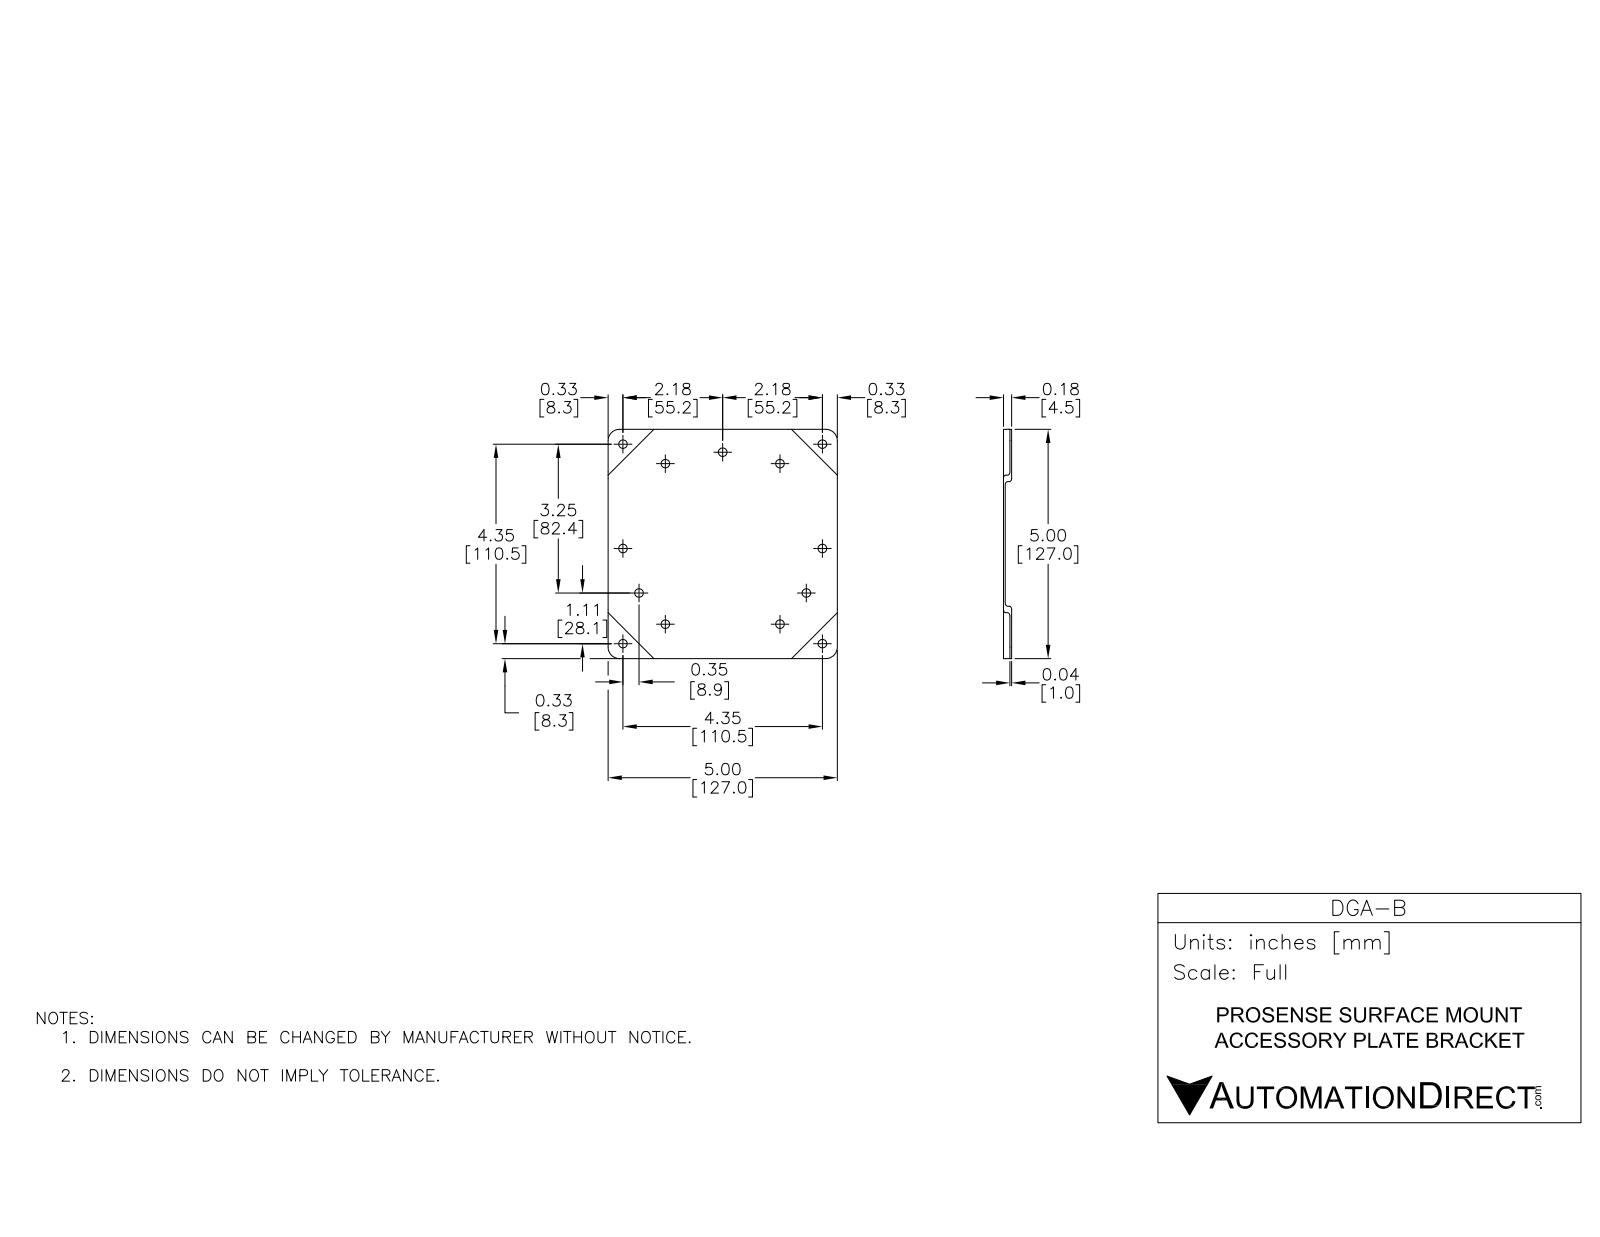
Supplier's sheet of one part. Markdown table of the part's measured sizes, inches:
| quantity | value |
| --- | --- |
| part name | DGA-B |
| STEP written by | SolidWorks 2017 (AUTOMOTIVE_DESIGN) |
| units | inches |
| bodies | 1 solid, 68 faces (22 planar, 46 cylindrical, 0 other) |
| overall size | 5 × 5 × 0.188 |
| volume | 1.987 in³ |
| surface area | 52.23 in² |
| round holes (diameter × count) | 0.187 × 13 |
| partial cylindrical surfaces (radius × count) | 0.05 × 16, 0.25 × 4 |
| main face-to-face distances | 0.078, 0.109, 0.187, 0.031, 5, 0.1, 5.556, 5.456, 5.656 |
| hole center spacings | 4.35, 1.018, 3.452, 4.033, 5.209, 0.859, 1.049, 1.175 |
